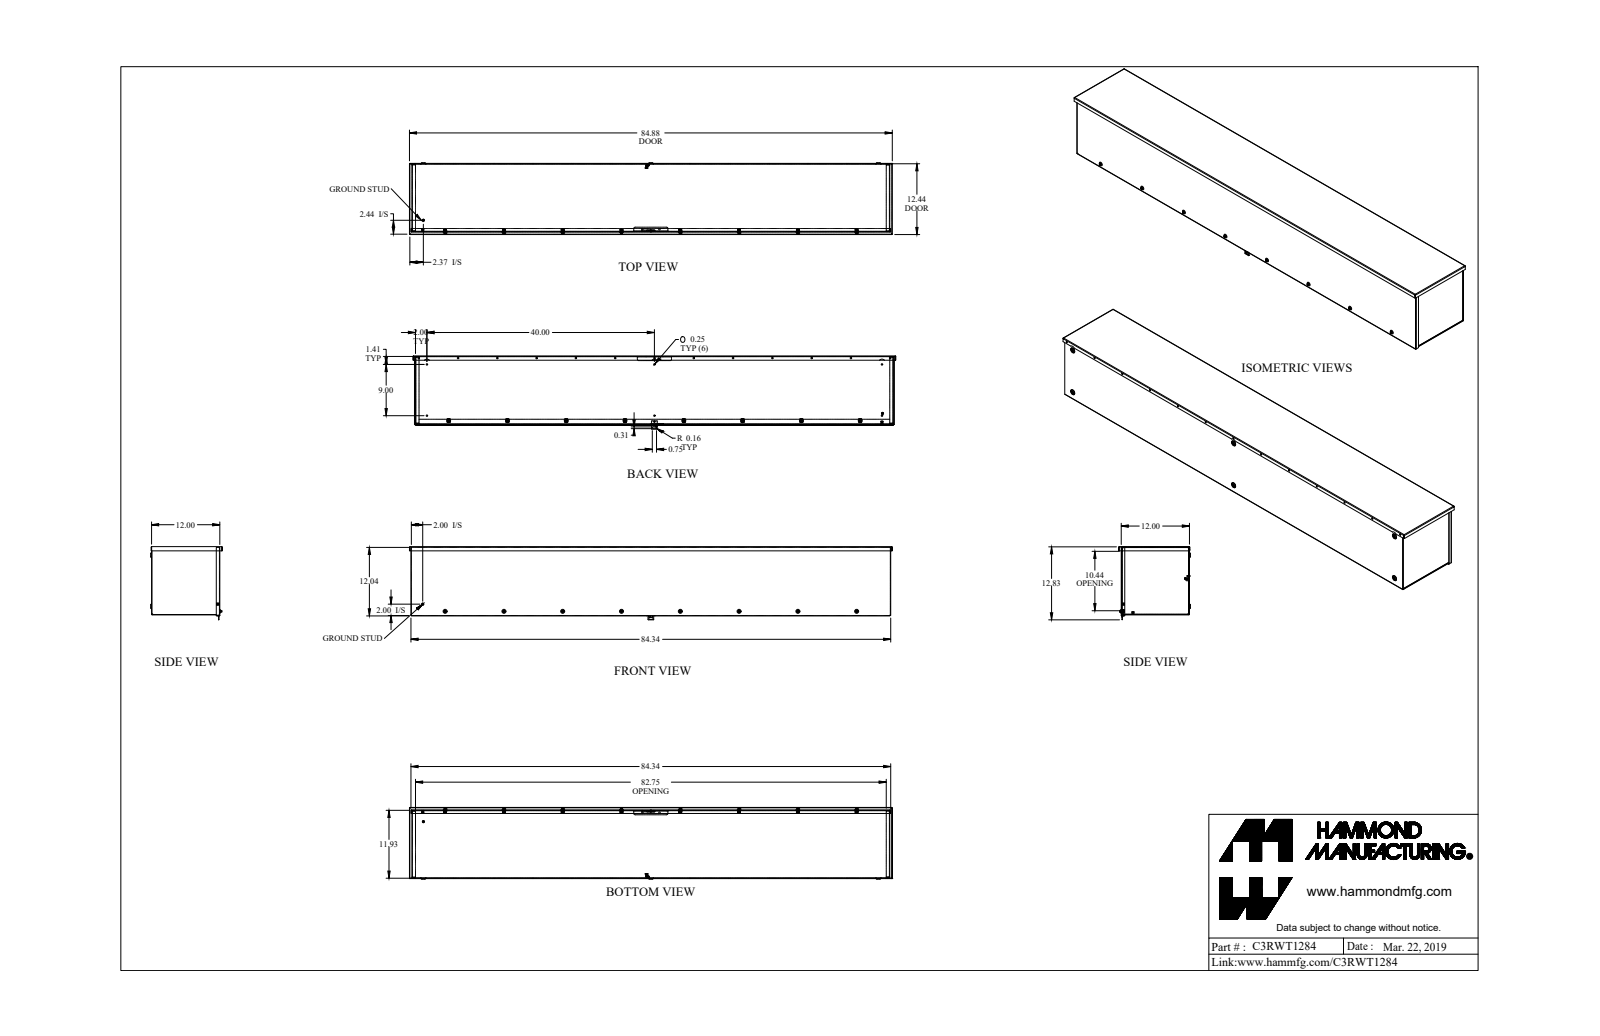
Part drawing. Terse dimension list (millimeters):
name: C3RWT1284_Default
written by: SolidWorks 2019 (CONFIG_CONTROL_DESIGN)
unit: mm
bodies: 38 solids, 1446 faces (783 planar, 463 cylindrical, 200 other)
size: 2155.8 × 326.9 × 319.9
volume: 5 504 000 mm³; area: 6 066 000 mm²
holes: 21× ⌀6.4, 10× ⌀4, 8× ⌀5.4, 8× ⌀5.8, 2× ⌀5.2, 1× ⌀3.2, 1× ⌀3.5, 1× ⌀5.1, 1× ⌀5.5
bosses: 9× ⌀4.8, 8× ⌀3.8, 2× ⌀9.5, 1× ⌀12.7, 1× ⌀9.3, 1× ⌀5.3, 1× ⌀3.9, 1× ⌀3.2
rounds: 32× R2, 32× R2.7, 18× R0.9, 18× R2.7, 16× R0.6, 16× R3.2, 8× R4.3, 8× R5.2
face distances: 1.8, 303, 304.8, 1.8, 301.1, 301.1, 303, 2131.8, 3.7, 2133.6
hole spacings: 175.4, 350.9, 525, 262.5, 526.3, 526.3, 701.7, 877.1
